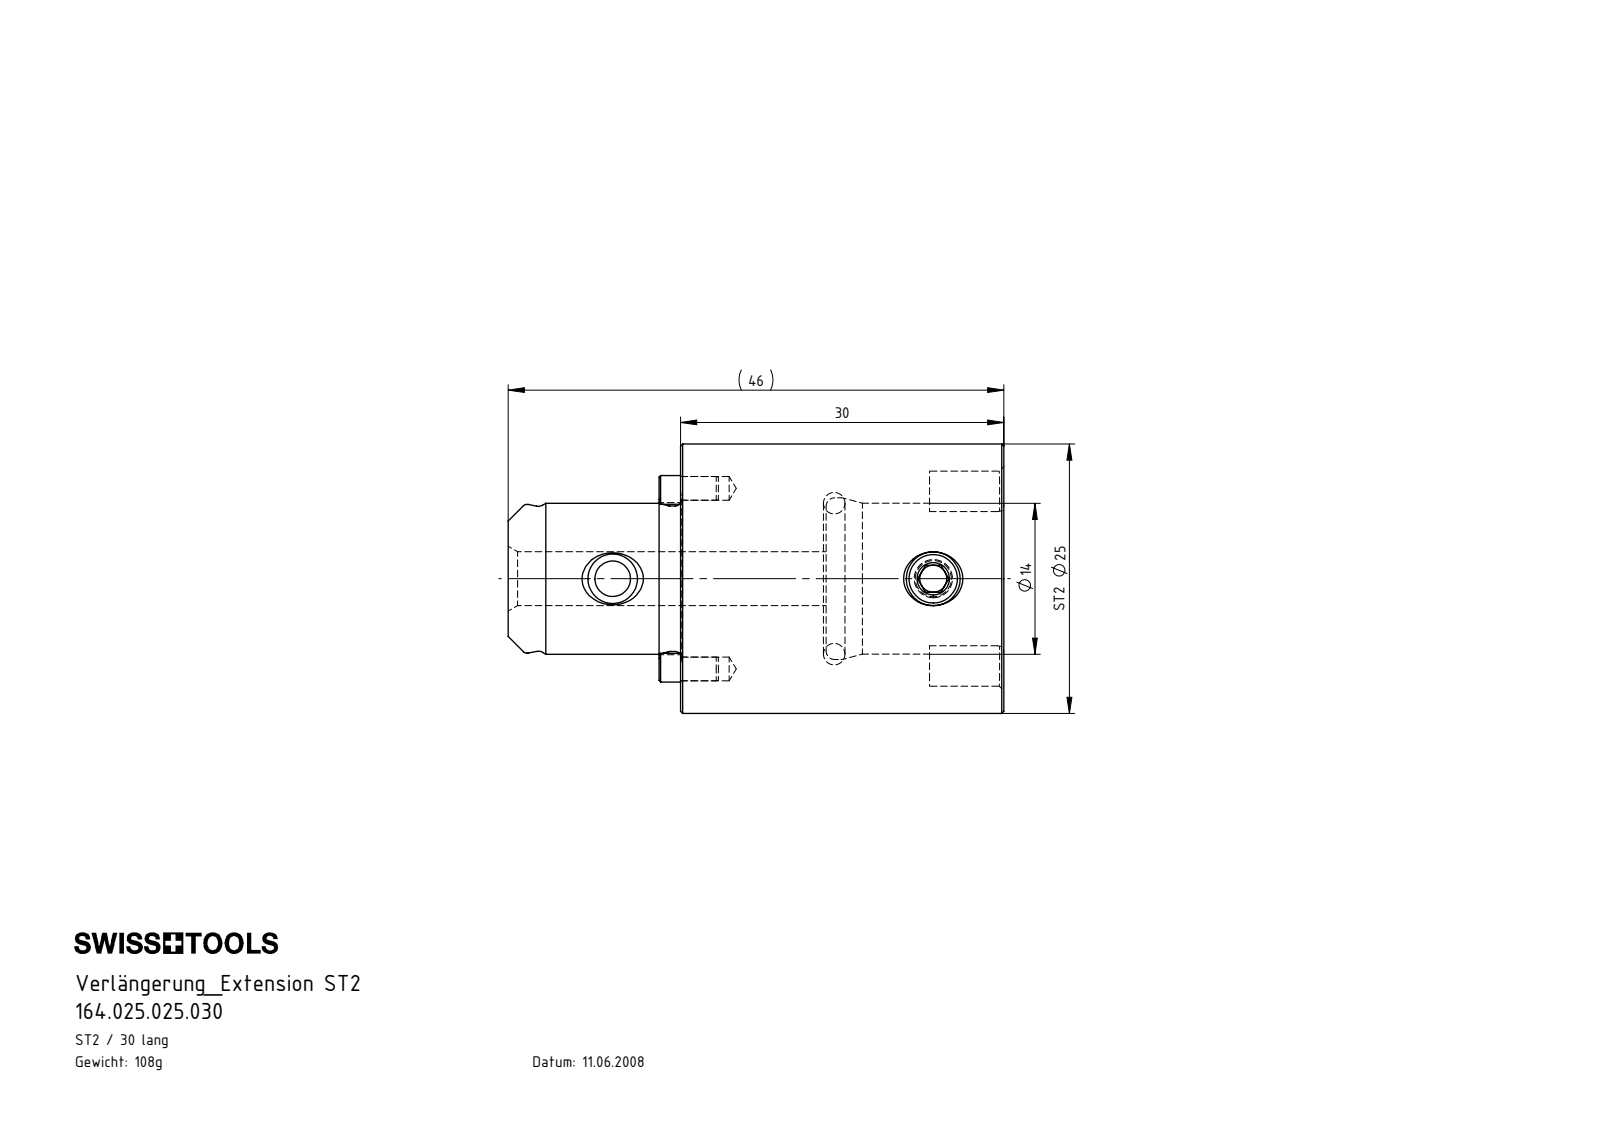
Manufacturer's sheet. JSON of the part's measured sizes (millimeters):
{"part_name": "ST2-ST2.K01.030_A; ST2-ST2.K01.030; ST2-ER1.001.006_A; ST2-ER2.001.006_A", "step_written_by": "SolidWorks 2015 (CONFIG_CONTROL_DESIGN)", "units": "millimeters", "bodies": {"solids": 4, "faces": 146, "planar": 26, "cylindrical": 43, "other": 77}, "overall_size": [46, 25, 25], "volume_mm3": 13730, "surface_area_mm2": 5575, "round_holes": [[2.2, 2], [3.3, 1], [4.5, 1], [5, 1], [14, 1], [15, 1]], "round_bosses_or_shafts": [[25, 1], [13.8, 1], [13.5, 1], [5, 1], [2.2, 1]], "partial_cylinders_radius": [[0.5, 4], [1.8, 2], [1.98, 2], [7.05, 1]], "face_to_face_distances": [30, 13.5, 16.5, 16, 29.5, 46, 11.78, 39.1, 23.1, 9.6], "hole_center_spacings": [8.38, 16.76, 29.75]}
